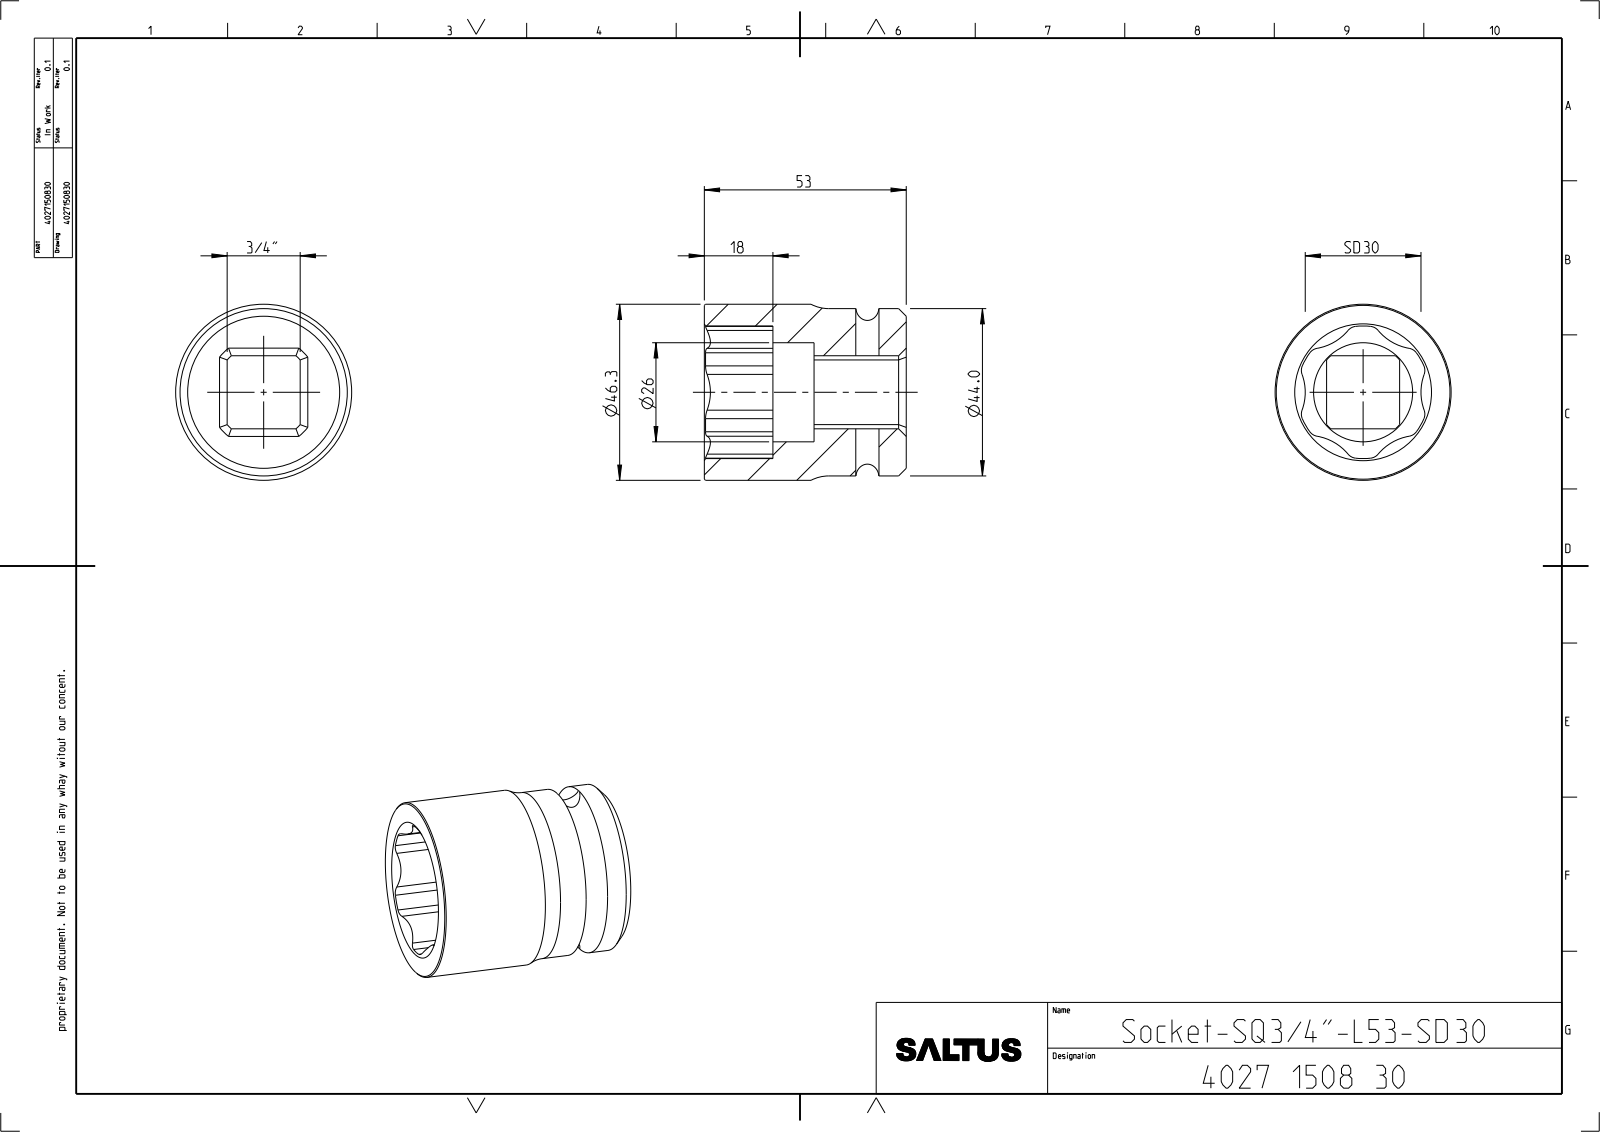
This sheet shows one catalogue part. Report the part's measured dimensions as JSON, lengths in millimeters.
{"part_name": "4027150830", "step_written_by": "CREO PARAMETRIC BY PTC INC, 2022414 (CONFIG_CONTROL_DESIGN)", "units": "millimeters", "bodies": {"solids": 1, "faces": 71, "planar": 15, "cylindrical": 40, "other": 16}, "overall_size": [53, 46.3, 46.3], "volume_mm3": 52504, "surface_area_mm2": 14926, "round_holes": [[6, 1], [26, 1]], "round_bosses_or_shafts": [[46.3, 1], [44, 1]], "partial_cylinders_radius": [[3, 12], [13.6, 6], [12.8, 1], [17.45, 1]], "face_to_face_distances": [19.18, 53, 35, 18, 24, 11, 29]}
